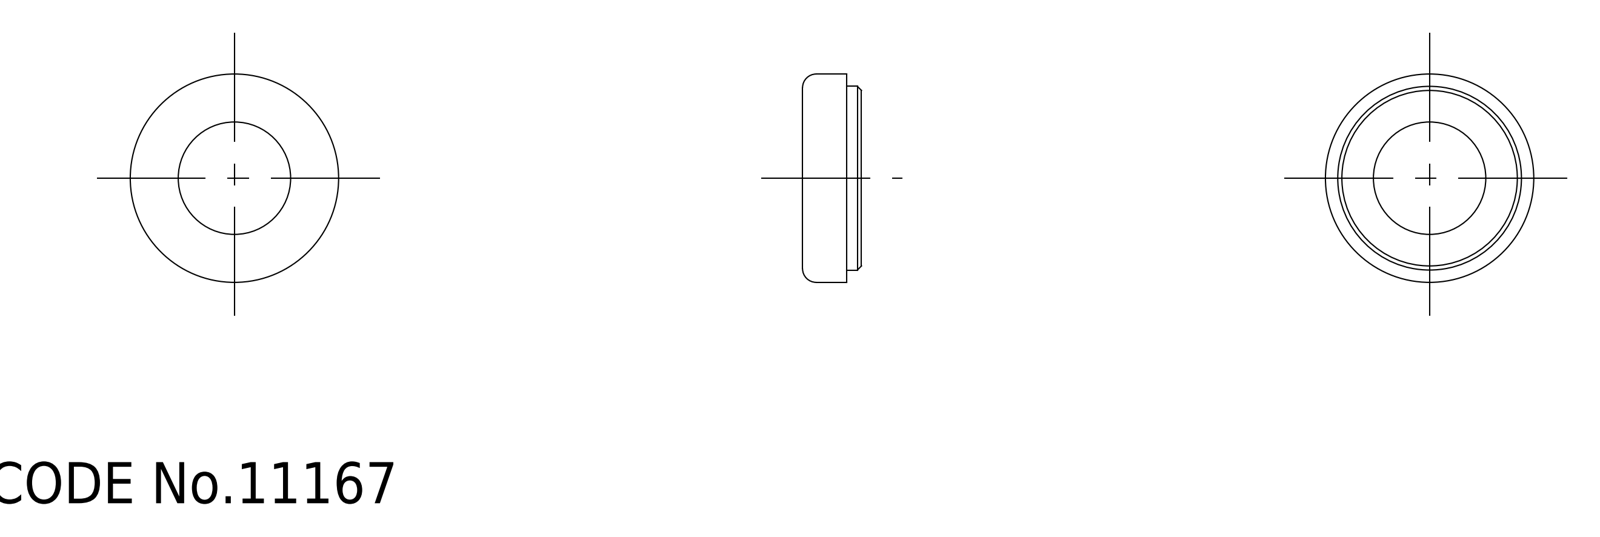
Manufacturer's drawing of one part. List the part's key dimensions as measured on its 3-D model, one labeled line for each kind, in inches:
Part name (STEP PRODUCT): packing; washer; TL_421_M8
STEP written by: SolidWorks 2015 (AUTOMOTIVE_DESIGN)
Units: inches
Bodies: 2 solids, 22 faces (6 planar, 12 cylindrical, 4 other)
Overall size (bounding box): 0.598 × 0.598 × 0.169
Volume: 0.03 in³ · Surface area: 1.39 in²
Round holes (diameter × count): ⌀0.323 ×1, ⌀0.52 ×1
Round bosses / shafts (diameter × count): ⌀0.598 ×1, ⌀0.528 ×1
Main face-to-face distances: 0.039, 0.169, 0.13, 0.126, 0.087, 0.043
